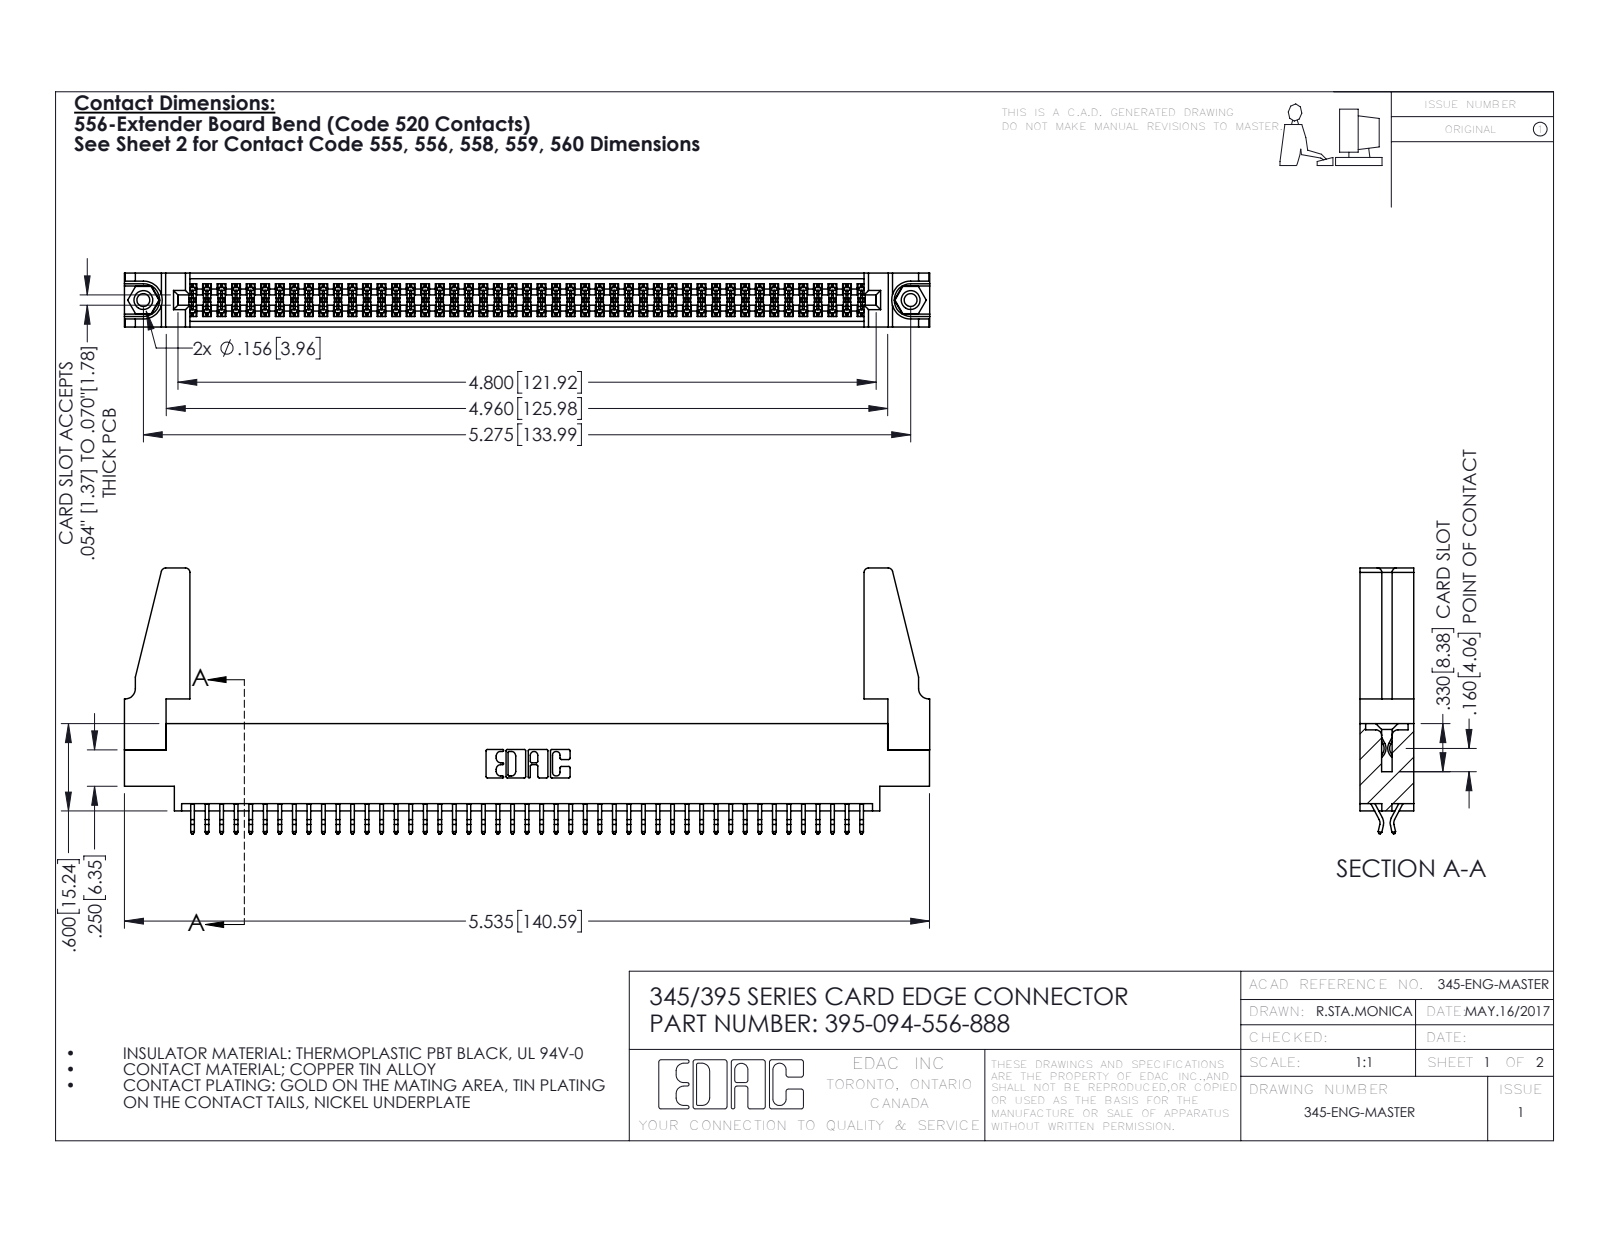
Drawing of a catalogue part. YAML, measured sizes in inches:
part_name: "395-094-556-888; 345 Part_0.170 Offset - 0.156 Dia-TH; 345-220-078_345-220-088; 345-292-001_556 Tail (+1 more)"
step_written_by: "SolidWorks 2016 (CONFIG_CONTROL_DESIGN)"
units: inches
bodies: {solids: 99, faces: 5518, planar: 3634, cylindrical: 1868, other: 16}
overall_size: [5.536, 1.827, 0.37]
volume: 1.028
surface_area: 36.22
round_holes:
  - {diameter: 0.089, count: 2}
  - {diameter: 0.125, count: 2}
  - {diameter: 0.156, count: 2}
  - {diameter: 0.064, count: 1}
round_bosses_or_shafts:
  - {diameter: 0.155, count: 2}
partial_cylinders:
  - {radius: 0.006, count: 141}
  - {radius: 0.01, count: 22}
  - {radius: 0.03, count: 8}
  - {radius: 0.007, count: 6}
  - {radius: 0.031, count: 6}
  - {radius: 0.026, count: 3}
  - {radius: 0.01, count: 2}
  - {radius: 0.014, count: 2}
face_to_face_distances: [0.072, 0.298, 0.37, 0.025, 0.098, 0.272, 0.2, 0.225, 0.175, 0.149]
hole_center_spacings: [0.27, 5.039, 5.275]
